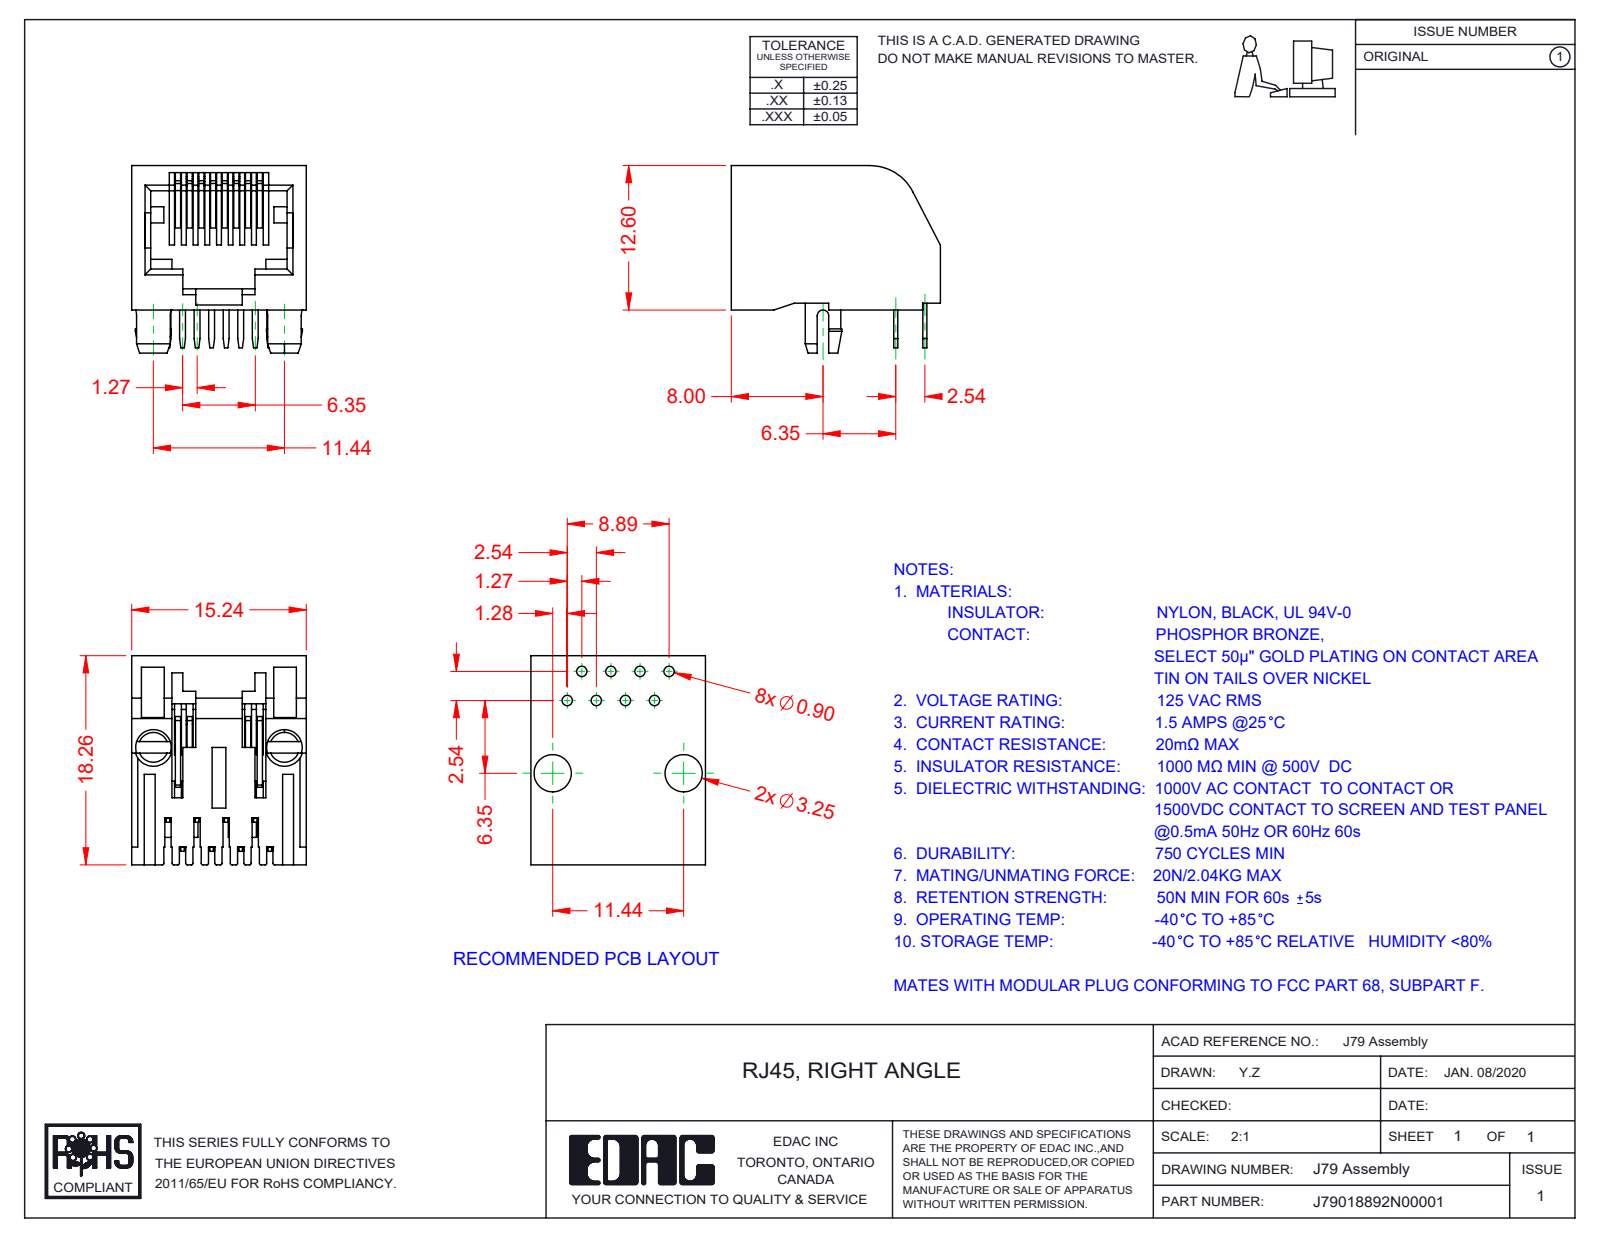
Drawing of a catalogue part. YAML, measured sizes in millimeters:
part_name: "79 Insulator; RJ79018892N00001; 79 Contacts"
step_written_by: "SolidWorks 2016 (CONFIG_CONTROL_DESIGN)"
units: millimeters
bodies: {solids: 9, faces: 574, planar: 424, cylindrical: 144, other: 6}
overall_size: [18.26, 16.36, 15.24]
volume: 1496
surface_area: 3263
round_bosses_or_shafts:
  - {diameter: 3.1, count: 2}
partial_cylinders:
  - {radius: 0.15, count: 16}
  - {radius: 0.5, count: 7}
  - {radius: 0.72, count: 3}
  - {radius: 0.36, count: 2}
  - {radius: 1.65, count: 2}
  - {radius: 1.8, count: 2}
  - {radius: 2.16, count: 2}
  - {radius: 0.2, count: 1}
face_to_face_distances: [15.24, 2.04, 0.6, 12, 0.36, 4.08, 1.25, 9.8, 2.2, 8.2]
